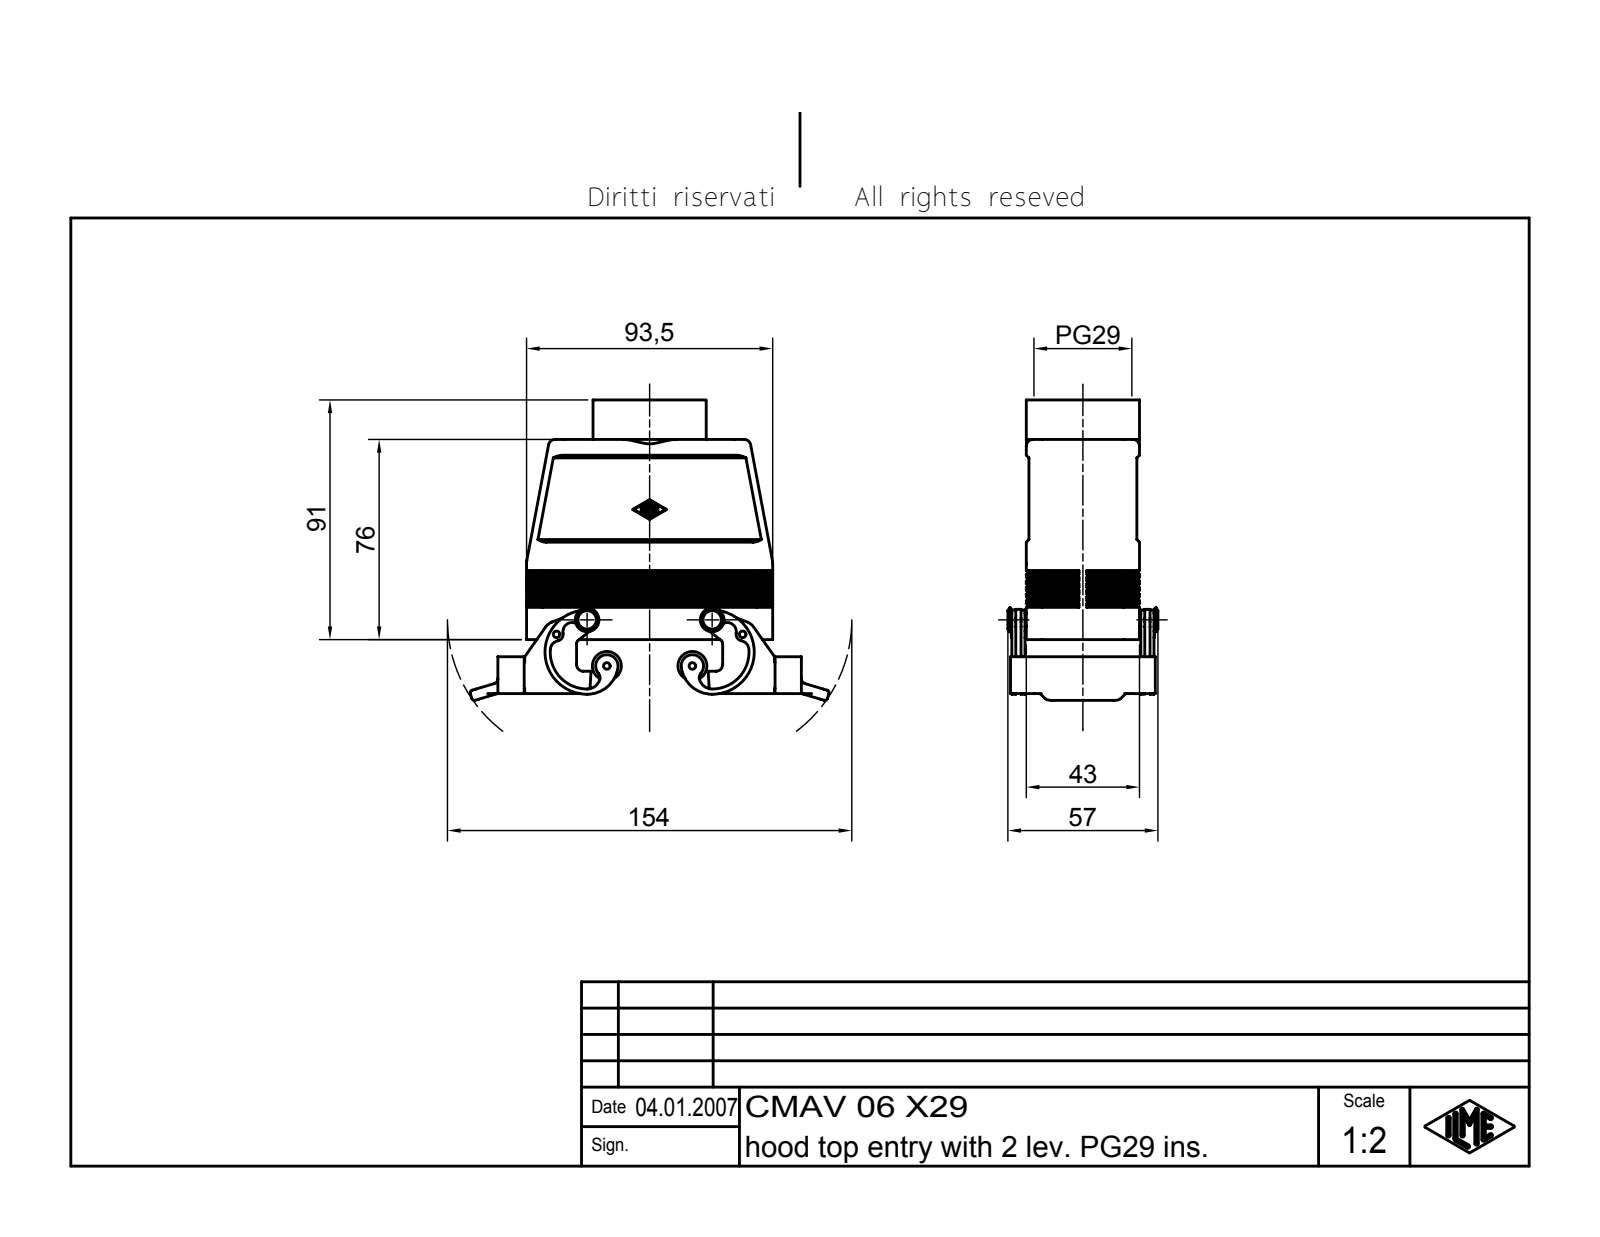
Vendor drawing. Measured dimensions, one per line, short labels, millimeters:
name: CAV Tüllengehäuse 2 Bügel für einen Einsatz Teil A
written by: Autodesk Inventor 7 (AUTOMOTIVE_DESIGN)
unit: mm
bodies: 1 solid, 945 faces (282 planar, 248 cylindrical, 415 other)
size: 136.29 × 114.08 × 57
volume: 97 343 mm³; area: 62 670 mm²
holes: 2× ⌀2.5, 1× ⌀33.48, 1× ⌀35.48
bosses: 2× ⌀11, 2× ⌀9, 2× ⌀5, 2× ⌀2, 1× ⌀43, 1× ⌀34.48
rounds: 14× R0.25, 12× R1, 10× R2, 10× R2.5, 10× R6, 8× R3, 4× R3.5, 4× R5
face distances: 3, 2, 42, 37, 40, 1, 39, 43, 5, 41
hole spacings: 70.7
